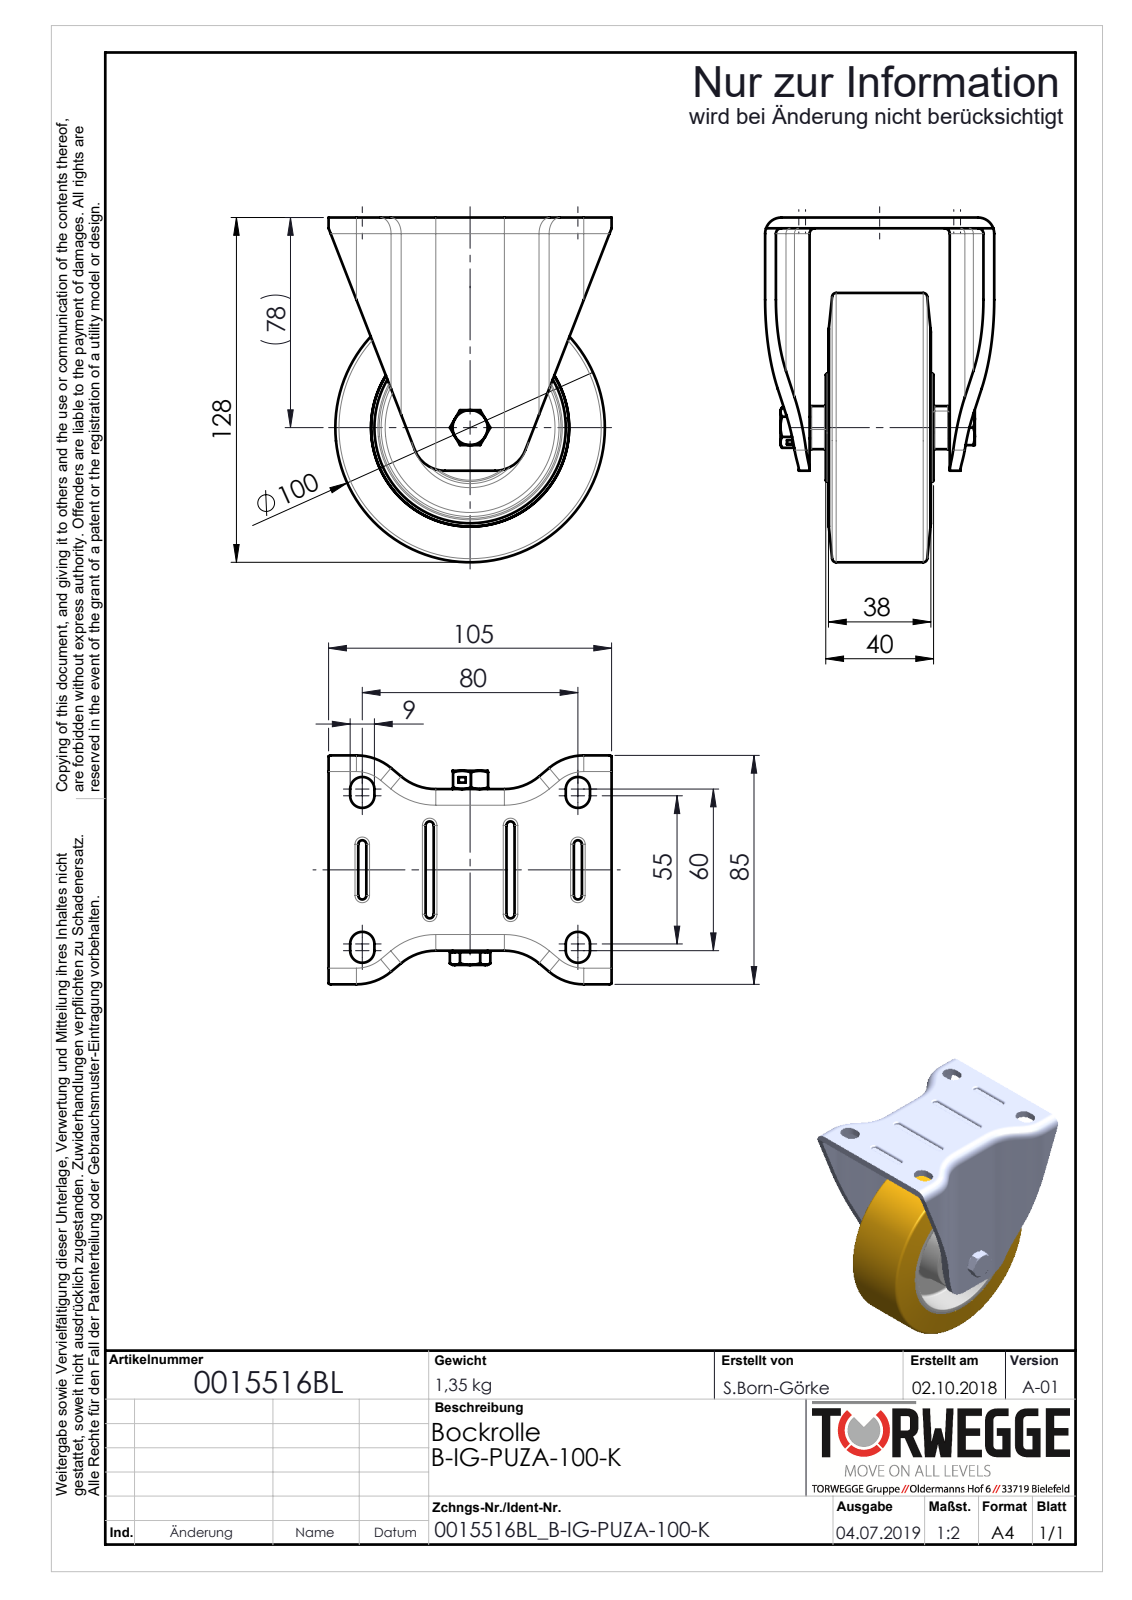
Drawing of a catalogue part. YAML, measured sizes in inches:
part_name: "0015516BL_B-IG-PUZA-100-K_(A-01)"
step_written_by: "SolidWorks 2018 (AUTOMOTIVE_DESIGN)"
units: inches
bodies: {solids: 0, faces: 306, planar: 98, cylindrical: 98, other: 110}
overall_size: [5.039, 4.134, 3.346]
round_holes:
  - {diameter: 0.268, count: 1}
  - {diameter: 0.315, count: 1}
  - {diameter: 0.323, count: 1}
  - {diameter: 0.327, count: 1}
  - {diameter: 0.472, count: 1}
  - {diameter: 1.102, count: 1}
  - {diameter: 1.26, count: 1}
round_bosses_or_shafts:
  - {diameter: 3.937, count: 1}
  - {diameter: 0.709, count: 1}
  - {diameter: 0.63, count: 1}
  - {diameter: 0.512, count: 1}
partial_cylinders:
  - {radius: 0.047, count: 8}
  - {radius: 0.079, count: 8}
  - {radius: 0.177, count: 8}
  - {radius: 0.236, count: 8}
  - {radius: 0.787, count: 8}
  - {radius: 0.63, count: 4}
  - {radius: 0.945, count: 4}
  - {radius: 0.472, count: 2}
face_to_face_distances: [0.157, 2.205, 0.886, 1.043, 1.319, 1.161, 2.362, 2.047, 0.276, 0.65]
